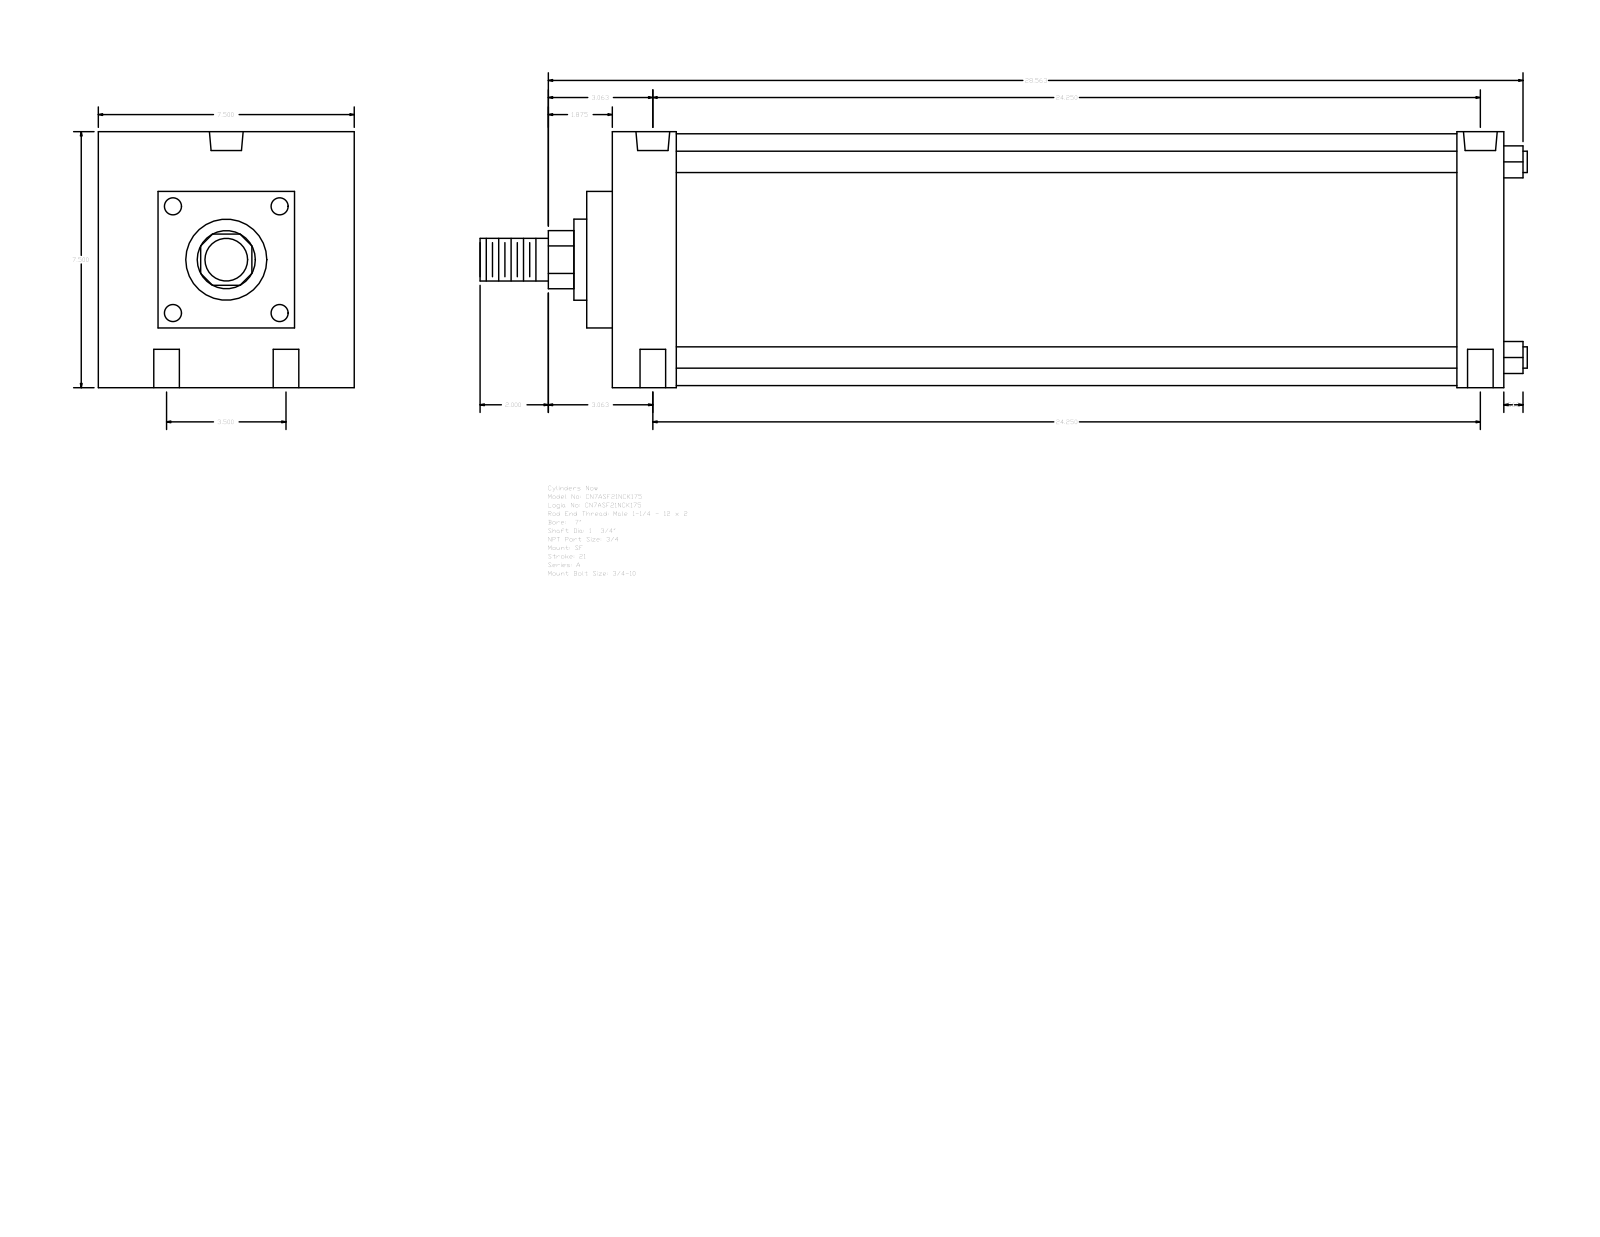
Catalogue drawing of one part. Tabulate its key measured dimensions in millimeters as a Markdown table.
| quantity | value |
| --- | --- |
| part name | A_SF__0700_1.75 |
| STEP written by | GSSL Pune (CONFIG_CONTROL_DESIGN) |
| units | millimeters |
| bodies | 0 solids, 93 faces (67 planar, 26 cylindrical, 0 other) |
| overall size | 779.46 × 190.5 × 190.5 |
| round holes (diameter × count) | 19.05 × 4, 15.08 × 2, 25.12 × 2 |
| round bosses / shafts (diameter × count) | 15.88 × 4, 187.32 × 1, 60.33 × 1, 44.45 × 1, 31.75 × 1 |
| partial cylindrical surfaces (radius × count) | 21.63 × 1 |
| main face-to-face distances | 190.5, 663.58, 146.05, 19.05, 47.63, 628.65, 581.02, 615.95, 34.93, 44.45 |
| hole center spacings | 44.45, 617.55, 615.95, 88.9, 622.33, 604.83 |
